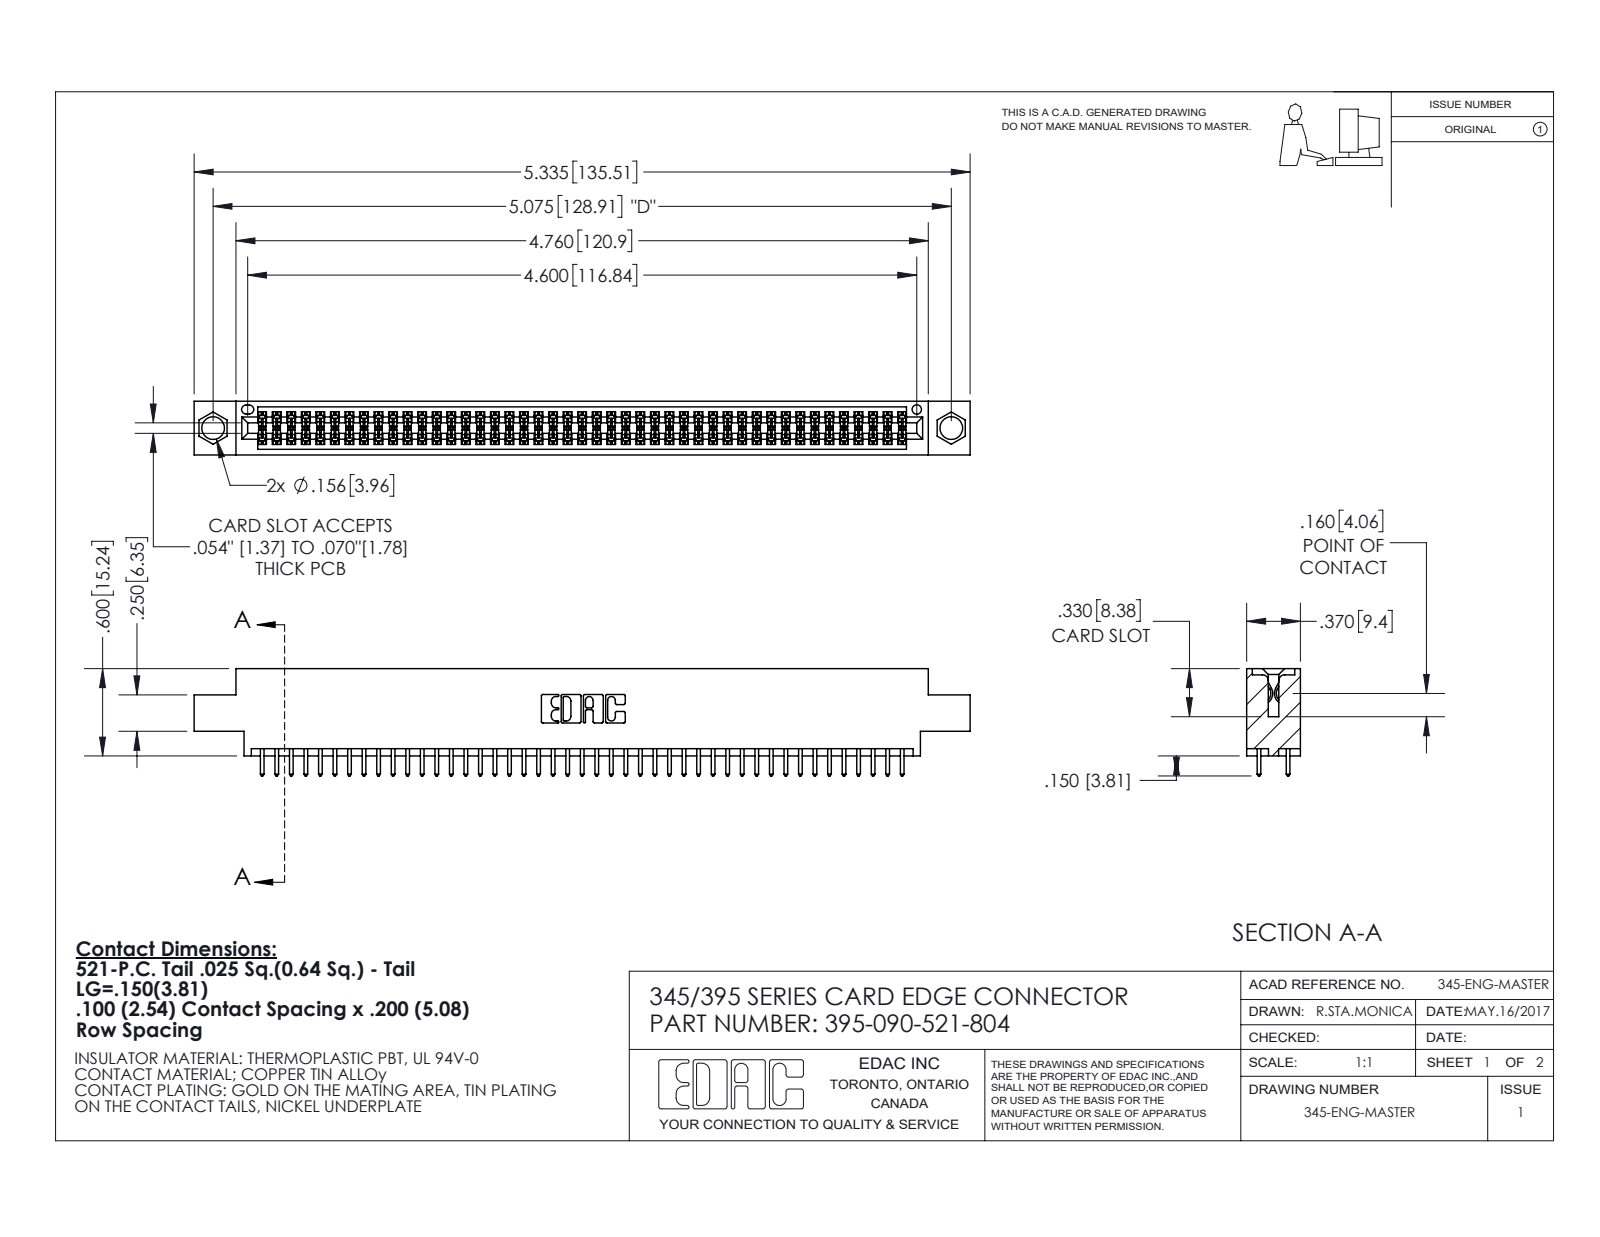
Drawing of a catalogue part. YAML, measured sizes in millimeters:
part_name: "345-292-001_345-293-121; 345 Part_0.170 Offset - 0.156 Dia-TI; 395-090-521-804"
step_written_by: "SolidWorks 2020 (CONFIG_CONTROL_DESIGN)"
units: millimeters
bodies: {solids: 91, faces: 4644, planar: 3068, cylindrical: 1576, other: 0}
overall_size: [135.5, 18.7, 9.4]
volume: 12900
surface_area: 18940
round_holes:
  - {diameter: 4, count: 2}
  - {diameter: 1.6, count: 1}
partial_cylinders:
  - {radius: 0.2, count: 180}
  - {radius: 0.3, count: 90}
  - {radius: 0.3, count: 22}
  - {radius: 0.2, count: 6}
  - {radius: 0.8, count: 6}
  - {radius: 0.7, count: 3}
  - {radius: 0.4, count: 2}
  - {radius: 0.5, count: 2}
face_to_face_distances: [1.8, 7.6, 5.1, 9.4, 2.5, 6.9, 0.6, 5.7, 4.4, 3.8]
hole_center_spacings: [6.9, 122.9, 128.9]
